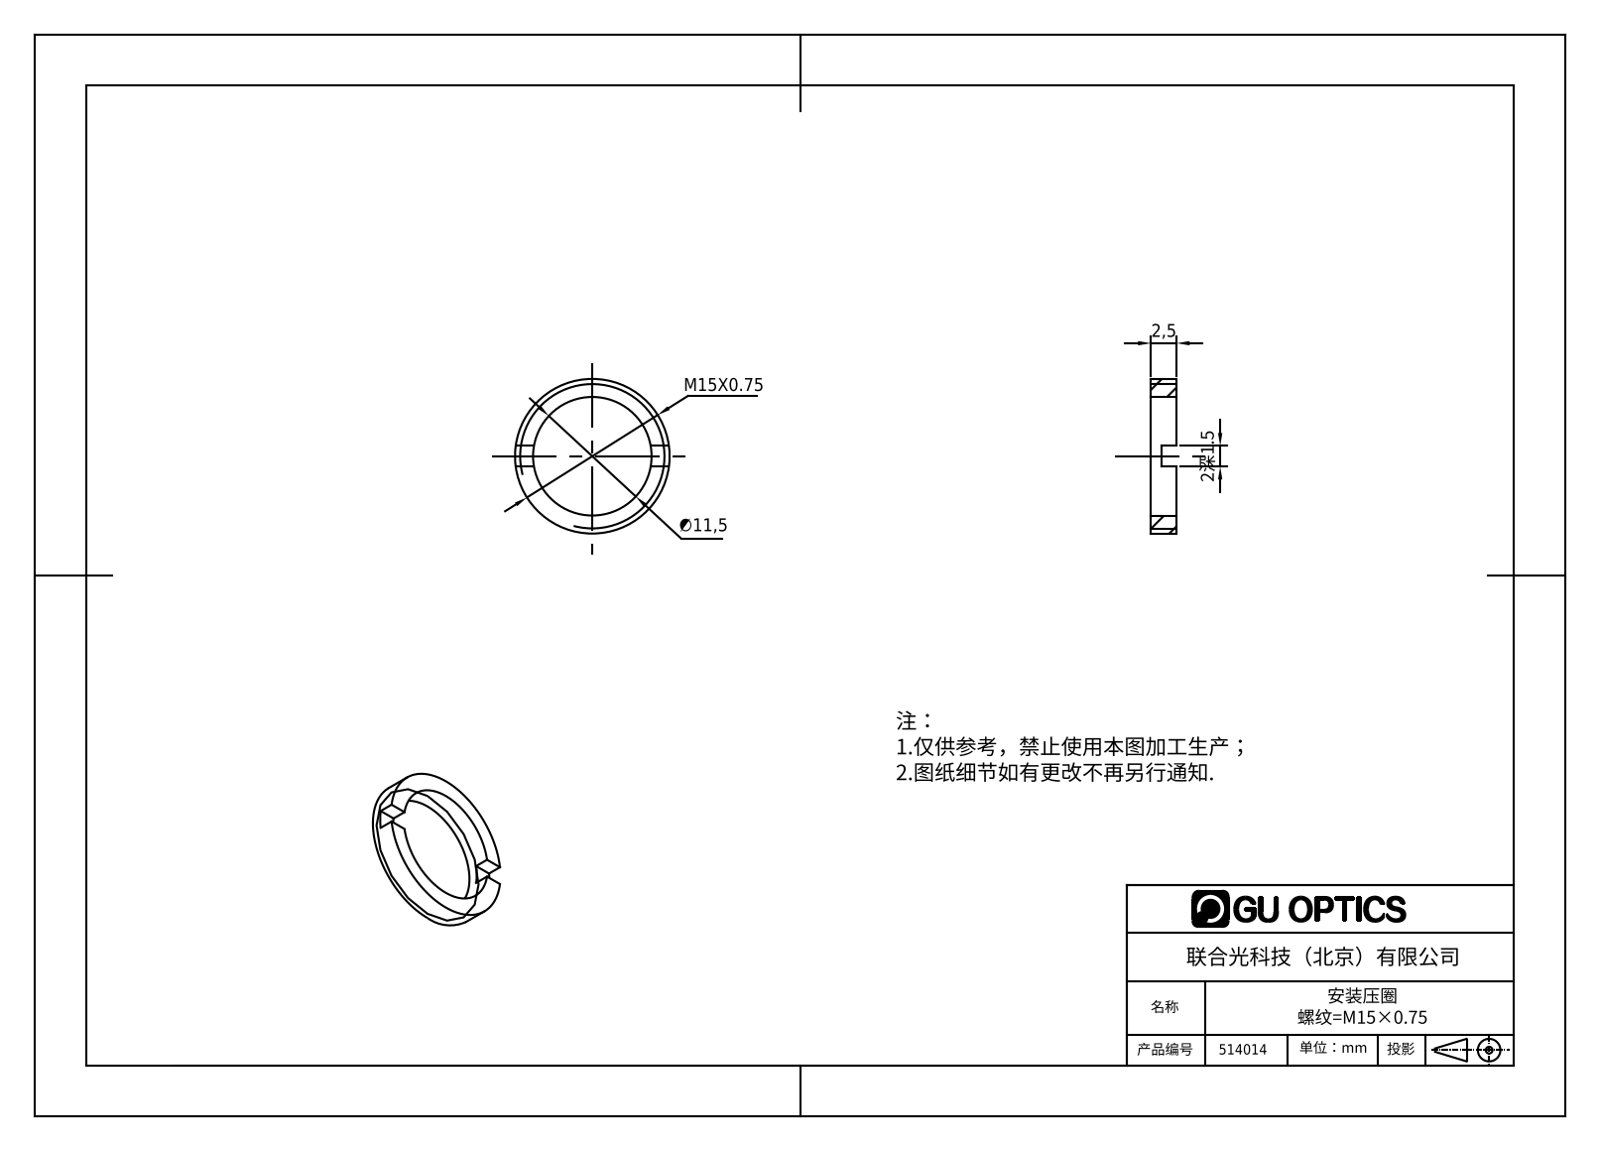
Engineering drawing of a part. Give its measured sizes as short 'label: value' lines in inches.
name: 514014
written by: SolidWorks 2016 (CONFIG_CONTROL_DESIGN)
unit: in
bodies: 1 solid, 13 faces (9 planar, 4 cylindrical, 0 other)
size: 0.591 × 0.591 × 0.098
volume: 0.01 in³; area: 0.546 in²
holes: 1× ⌀0.453
bosses: 1× ⌀0.591
face distances: 0.098, 0.039, 0.059, 0.079
